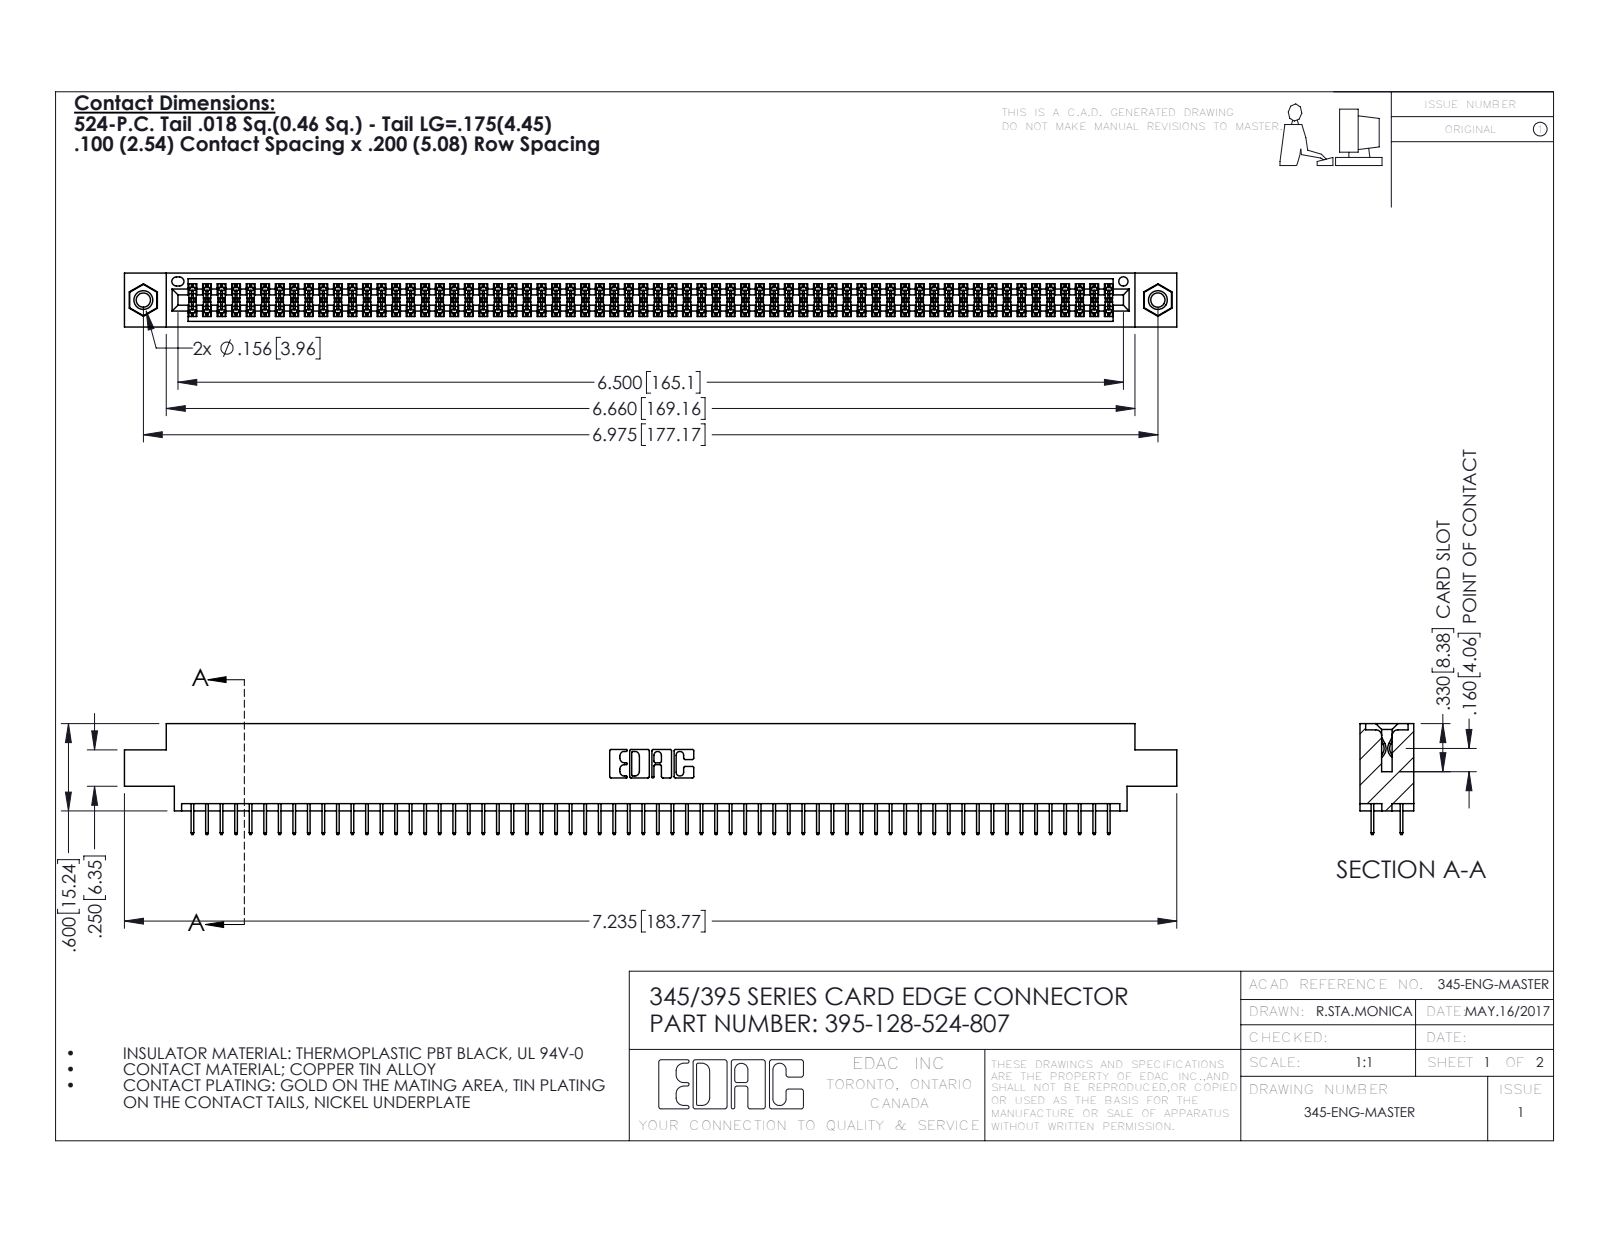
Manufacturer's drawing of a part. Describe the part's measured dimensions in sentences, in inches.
The part is named "345-250-001_345-250-005-103; 345 Part_0.170 Offset - 0.156 Dia-TI; 395-128-524-807; 345-292-001_345-293-124". Its 3-D file was written by "SolidWorks 2016 (CONFIG_CONTROL_DESIGN)". It is 131 solids with 7102 faces: 5108 planar, 1978 cylindrical and 16 other. Overall it measures 7.235 by 0.762 by 0.37 inches. Its volume is 1.082 cubic inches and its surface area 40.77 square inches. Round holes: 2 of diameter 0.098, 2 of diameter 0.125, 2 of diameter 0.156, 1 of diameter 0.064. Round bosses or shafts: 2 of diameter 0.155. Partial cylindrical surfaces (rounded edges, fillets, slot ends): 192 of radius 0.006, 22 of radius 0.01, 6 of radius 0.007, 6 of radius 0.031, 3 of radius 0.026, 2 of radius 0.014, 2 of radius 0.019, 2 of radius 0.022. The main face-to-face distances are 0.072, 0.298, 0.2, 0.37, 0.098, 0.272, 0.025, 0.225, 0.072, 0.175. The hole center spacings are 0.27, 6.739, 6.975.
